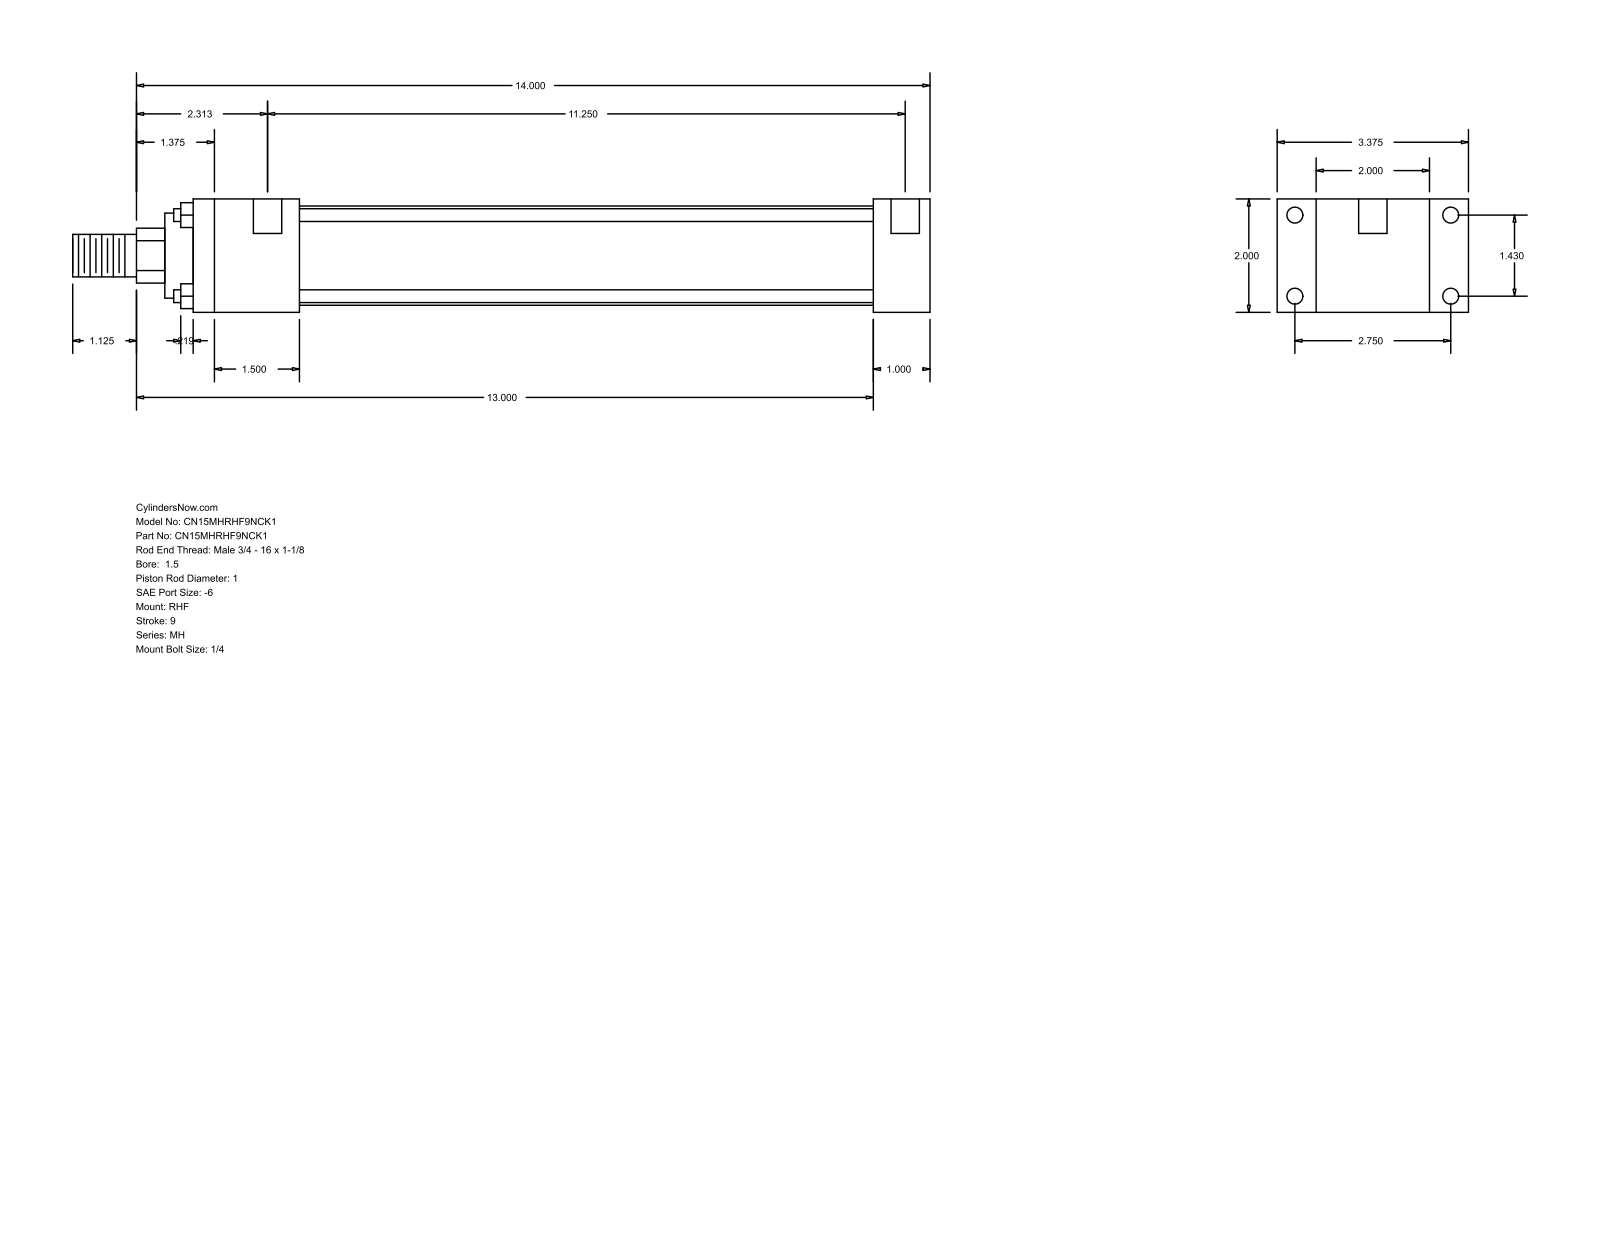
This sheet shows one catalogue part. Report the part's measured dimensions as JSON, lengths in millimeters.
{"part_name": "MH_RHF__0150_1", "step_written_by": "GSSL Pune (CONFIG_CONTROL_DESIGN)", "units": "millimeters", "bodies": {"solids": 0, "faces": 88, "planar": 60, "cylindrical": 28, "other": 0}, "overall_size": [384.18, 85.72, 50.8], "round_holes": [[5.56, 4], [7.14, 4], [12.7, 2]], "round_bosses_or_shafts": [[5.71, 4], [44.45, 1], [38.1, 1], [25.4, 1], [19.05, 1]], "partial_cylinders_radius": [[12.29, 1]], "face_to_face_distances": [50.8, 25.4, 17.46, 68.26, 85.72, 330.2, 304.8, 47.63, 257.17, 282.57], "hole_center_spacings": [36.32, 69.84, 78.72, 288.93, 3.18, 285.75]}
